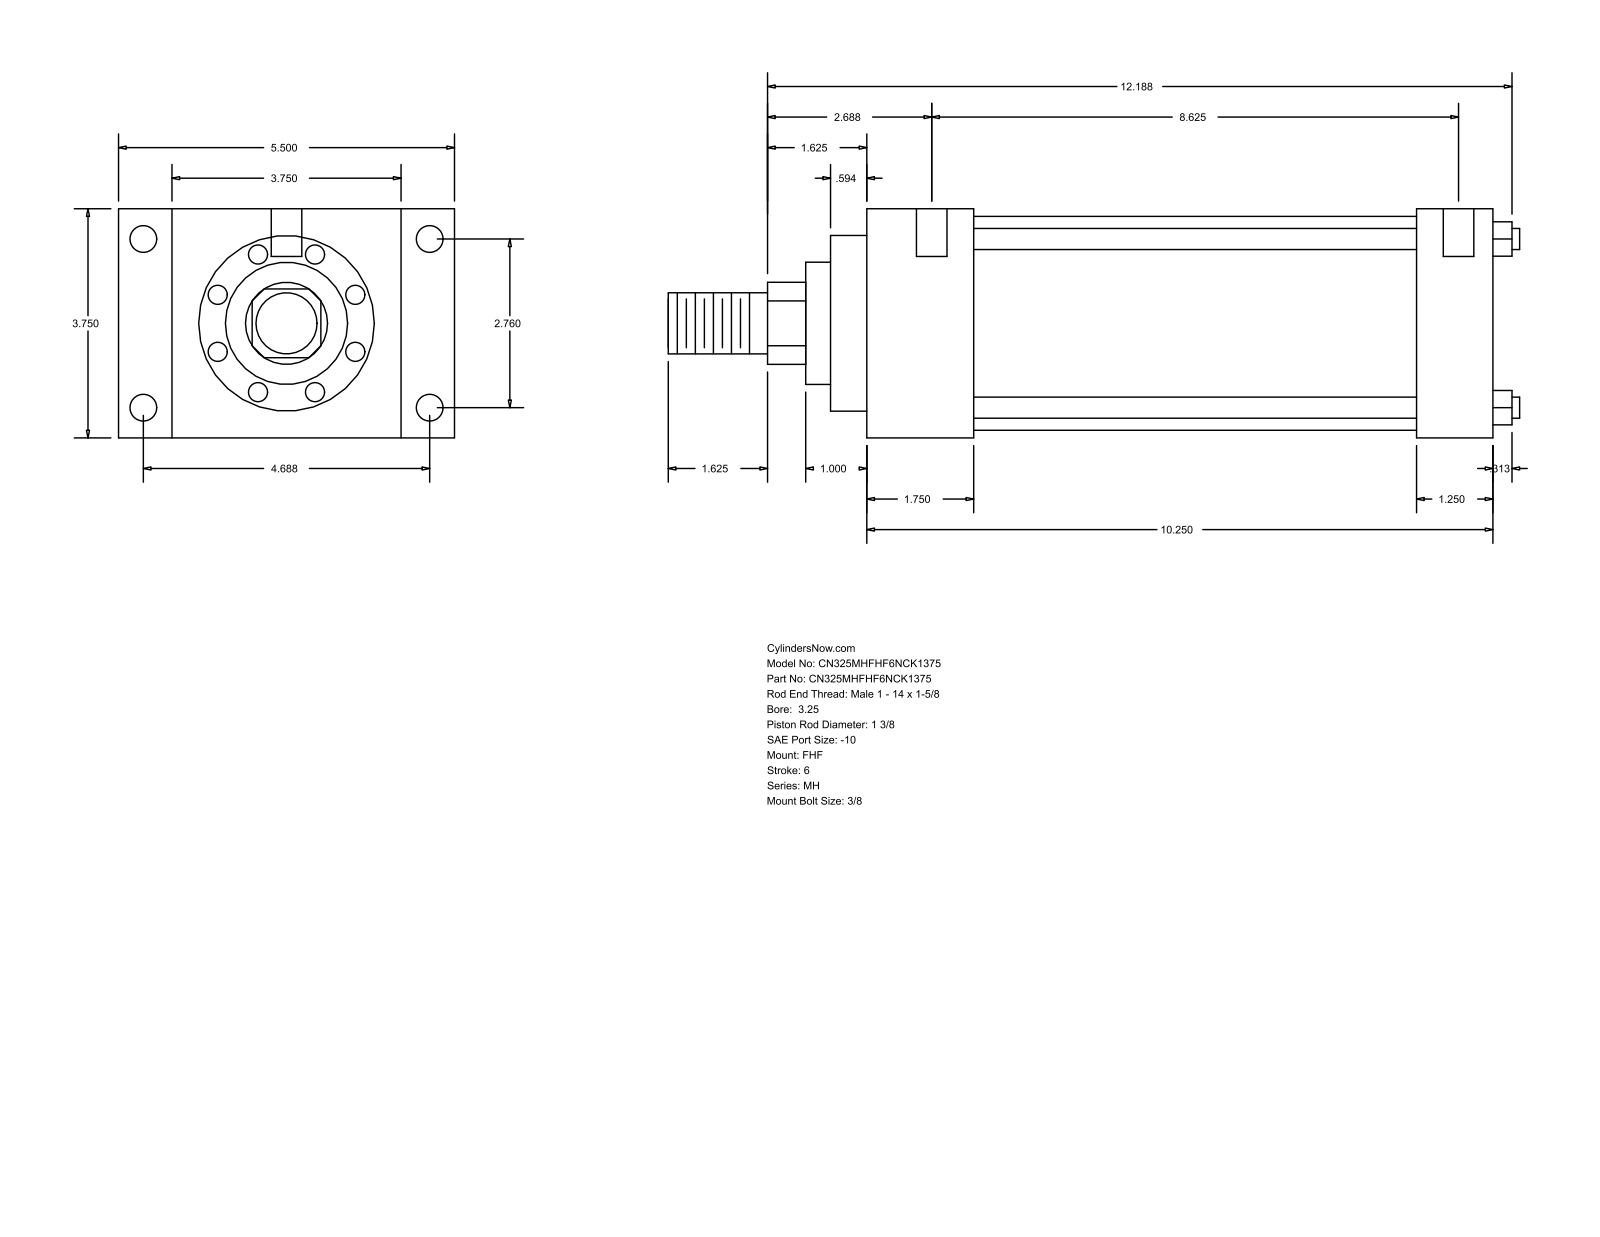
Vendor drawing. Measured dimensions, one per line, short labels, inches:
name: MH_FHF__0325_1.375
written by: GSSL Pune (CONFIG_CONTROL_DESIGN)
unit: in
bodies: 0 solids, 90 faces (61 planar, 29 cylindrical, 0 other)
size: 13.937 × 5.5 × 3.75
holes: 4× ⌀0.219, 4× ⌀0.438, 2× ⌀0.5
bosses: 4× ⌀0.345, 1× ⌀3.5, 1× ⌀2.875, 1× ⌀2, 1× ⌀1.375, 1× ⌀1
rounds: 1× R0.672
face distances: 3.75, 10.25, 1.75, 8.5, 0.875, 4.625, 5.5, 9, 7.25, 1.25
hole spacings: 2.76, 4.687, 5.439, 8.875, 0.063, 0.187, 8.625, 8.688
